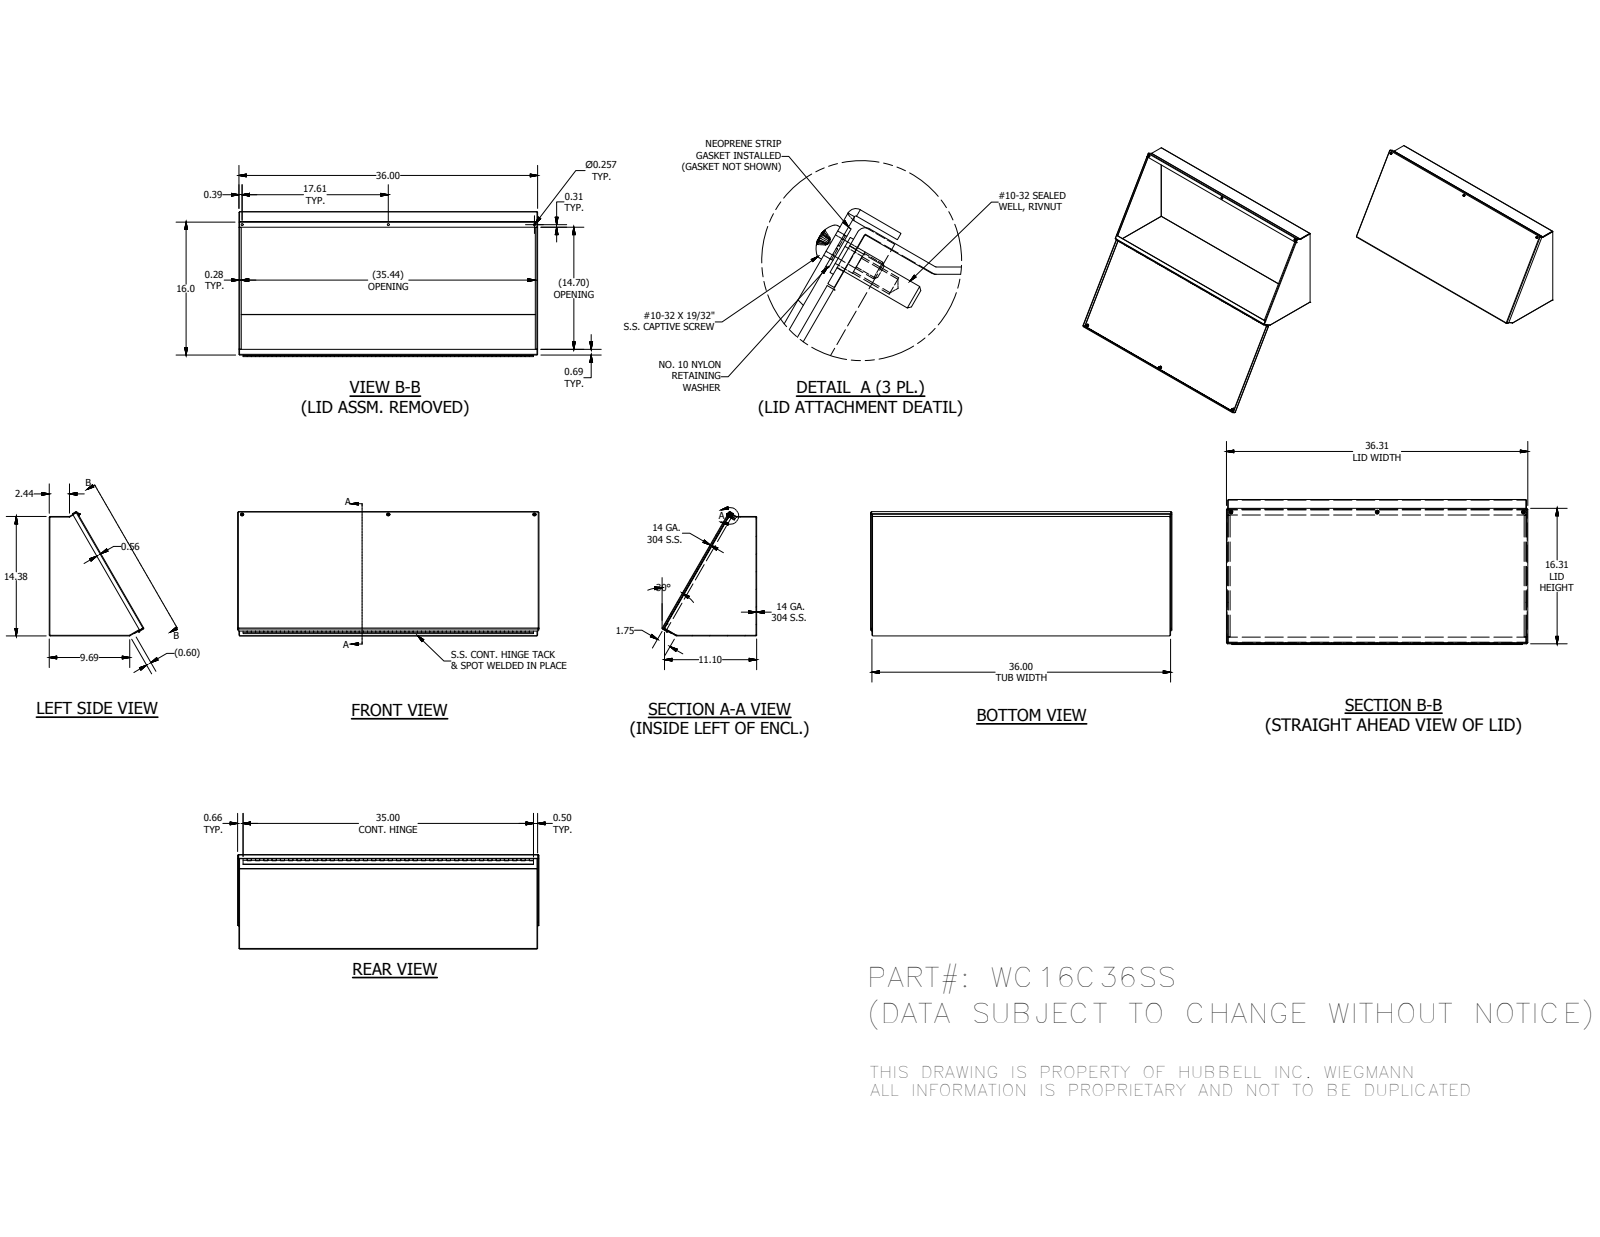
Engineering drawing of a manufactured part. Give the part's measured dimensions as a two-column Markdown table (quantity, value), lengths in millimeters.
| quantity | value |
| --- | --- |
| part name | WC16C36SSBTB; WC16C36SSLID; WC16CSSLS; WC16CSSRS (+8 more) |
| STEP written by | Autodesk Inventor 2014 (AUTOMOTIVE_DESIGN) |
| units | millimeters |
| bodies | 16 solids, 717 faces (436 planar, 207 cylindrical, 74 other) |
| overall size | 922.34 × 380 × 289.23 |
| volume | 2 392 000 mm³ |
| surface area | 2 598 000 mm² |
| round holes (diameter × count) | 3.96 × 3, 4.98 × 3, 6.53 × 3, 7.06 × 3, 7.14 × 3, 2.96 × 1 |
| round bosses / shafts (diameter × count) | 11.51 × 3, 10.31 × 3, 9.47 × 3, 6.3 × 3, 4.83 × 3, 5.08 × 1, 2.54 × 1 |
| partial cylindrical surfaces (radius × count) | 0.4 × 12, 2.28 × 12, 2.27 × 3 |
| main face-to-face distances | 1.88, 912.52, 910.64, 914.4, 363.25, 361.37, 1.87, 365.12, 363.24, 2.94 |
| hole center spacings | 447.37, 894.74, 1.41 |
